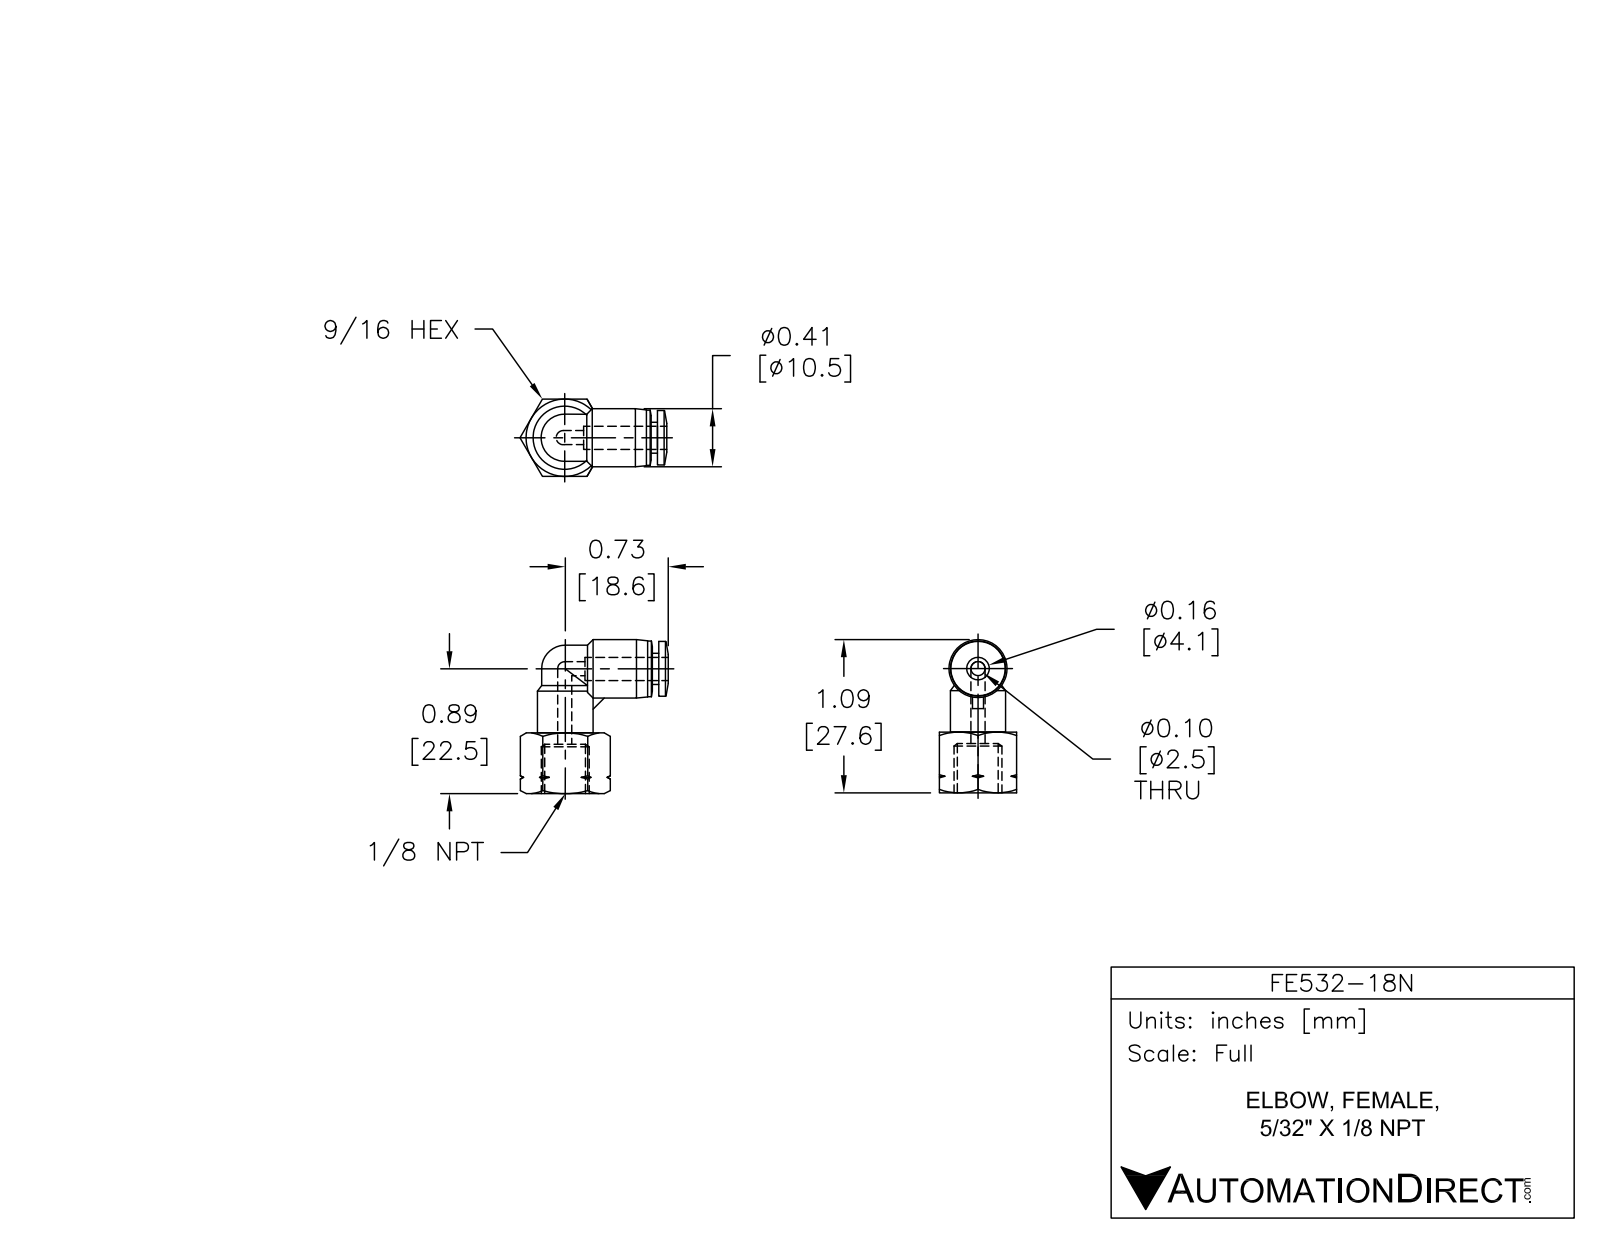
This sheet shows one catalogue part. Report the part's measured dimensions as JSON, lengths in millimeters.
{"part_name": "FE532-18N", "step_written_by": "SolidWorks 2015 (AUTOMOTIVE_DESIGN)", "units": "millimeters", "bodies": {"solids": 1, "faces": 83, "planar": 16, "cylindrical": 21, "other": 46}, "overall_size": [27.8, 26.6, 14], "volume_mm3": 3020, "surface_area_mm2": 2442, "round_holes": [[2.5, 2], [4.3, 1]], "round_bosses_or_shafts": [[10, 2], [10.5, 1], [9.9, 1], [5.6, 1]], "partial_cylinders_radius": [[4.2, 2]], "face_to_face_distances": [14, 2, 11, 9, 1.1, 11.9, 13.1, 6, 8, 11.1]}
